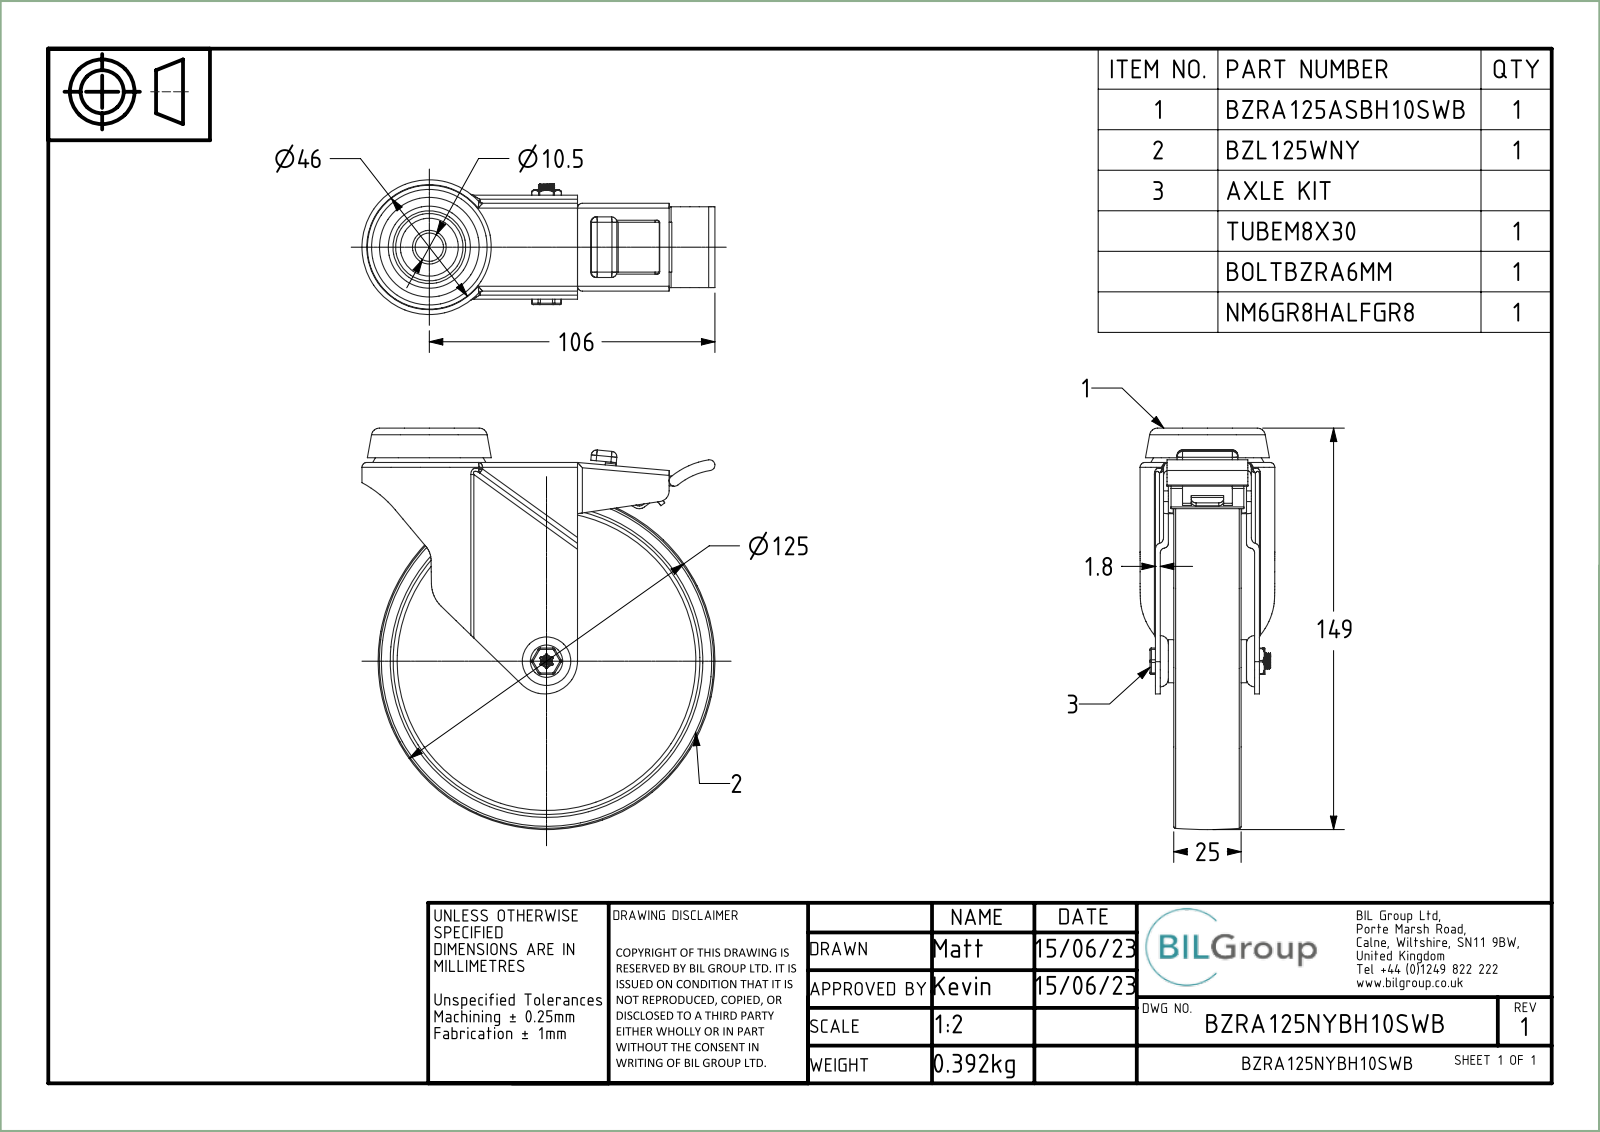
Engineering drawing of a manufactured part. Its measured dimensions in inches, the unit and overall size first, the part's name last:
Units: inches
Overall size (bounding box): 5.866 × 5.157 × 1.969
Round holes (diameter × count): ⌀0.236 ×1, ⌀0.248 ×1, ⌀0.252 ×1, ⌀0.323 ×1, ⌀0.327 ×1, ⌀0.413 ×1, ⌀0.416 ×1, ⌀1.102 ×1, ⌀1.535 ×1
Round bosses / shafts (diameter × count): ⌀0.709 ×1, ⌀0.63 ×1, ⌀0.581 ×1, ⌀0.315 ×1, ⌀0.313 ×1, ⌀0.197 ×1
Partial cylindrical surfaces — rounded edges, fillets, slot ends (radius × count): R0.039 ×23, R0.071 ×23, R0.02 ×14, R0.035 ×11, R0.079 ×11, R0.016 ×6, R0.083 ×1, R0.09 ×1
Main face-to-face distances: 0.197, 0.071, 1.331, 0.591, 0.118, 0.661, 0.858, 0.189, 0.472, 0.669
Volume: 9.05 in³ · Surface area: 139.4 in²
Bodies: 9 solids, 627 faces (214 planar, 250 cylindrical, 163 other)
Part name (STEP PRODUCT): BZRA125ASBH10SWB; ZINC PLATED PRESSED STEEL HEAD; ZINC PLATED PRESSED STEEL FORKS; ZINC PLATED PRESSED STEEL BRAKE (+8 more)
STEP written by: Spatial InterOp 3D (CONFIG_CONTROL_DESIGN)
